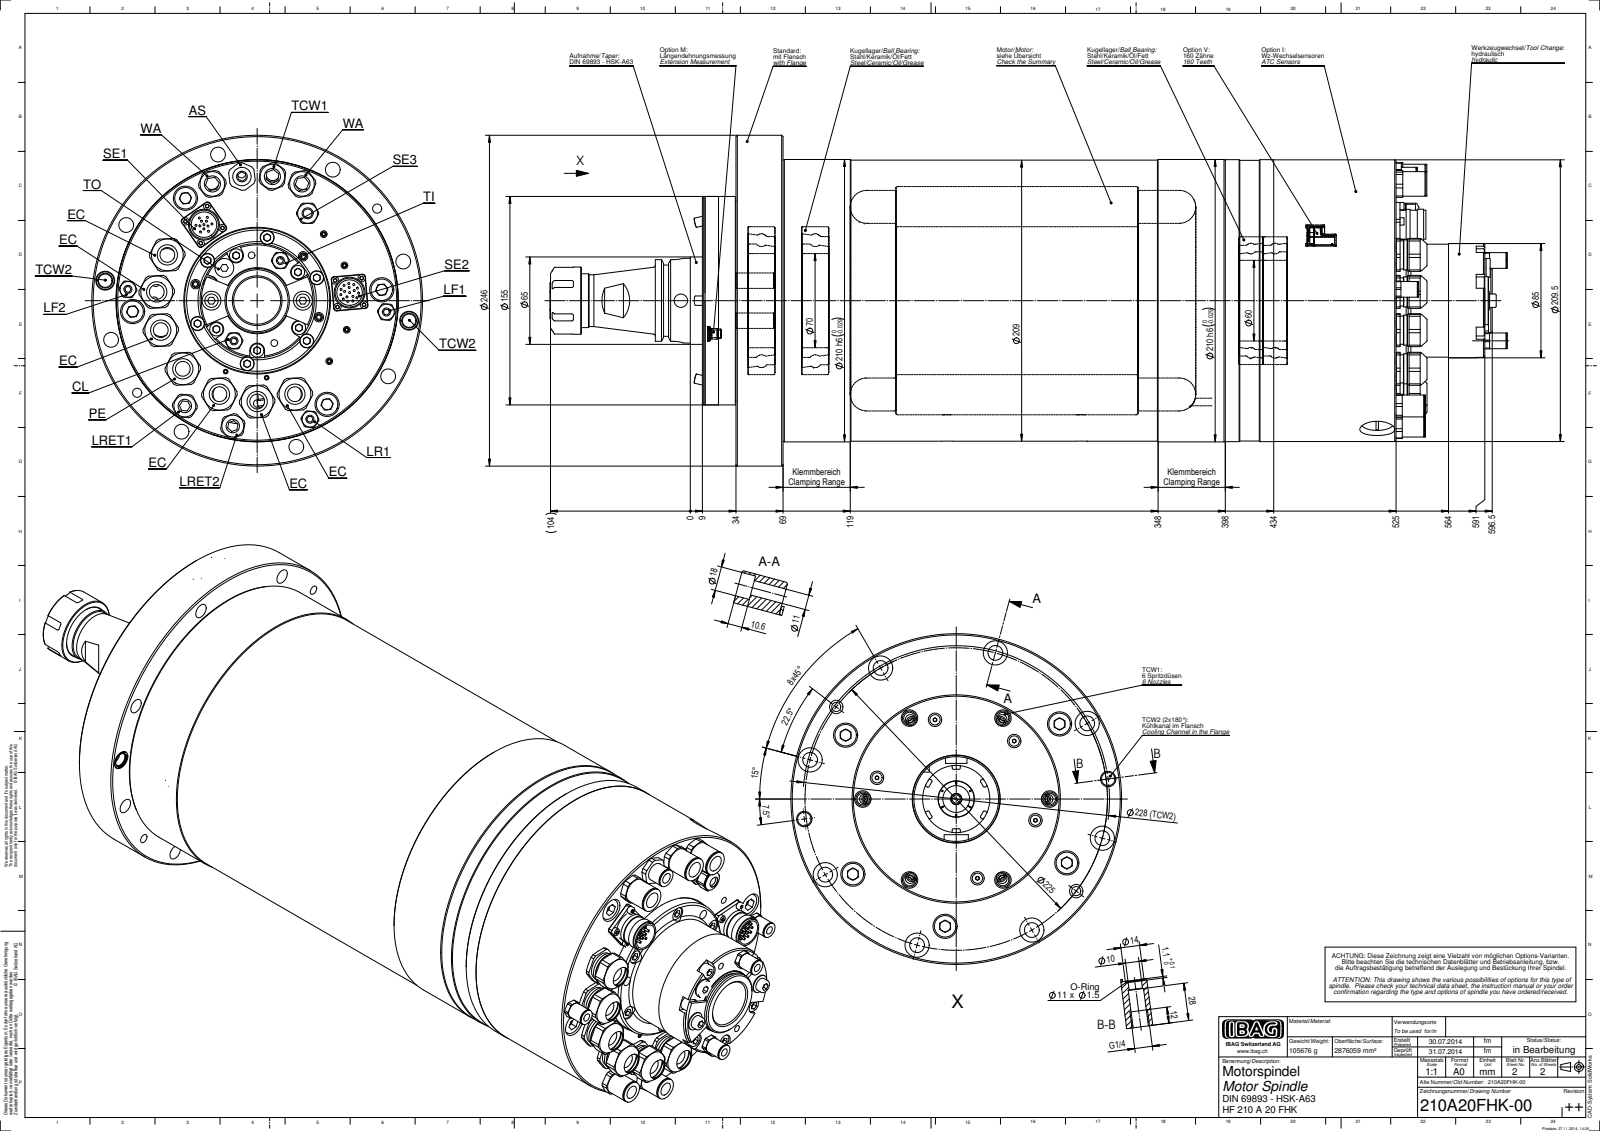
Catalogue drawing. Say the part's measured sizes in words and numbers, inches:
The part is named "210A20FHK-00". Its 3-D file was written by "SolidWorks 2014 (CONFIG_CONTROL_DESIGN)". It is 0 solids with 1647 faces: 619 planar, 704 cylindrical and 324 other. Overall it measures 28.037 by 9.685 by 9.685 inches. Round holes: 17 of diameter 0.433, 17 of diameter 0.709, 12 of diameter 0.197, 7 of diameter 0.394, 7 of diameter 0.594, 7 of diameter 0.839, 6 of diameter 0.409, 5 of diameter 0.236, 5 of diameter 1.181, 3 of diameter 0.276, 3 of diameter 0.413, 3 of diameter 0.472. Round bosses or shafts: 29 of diameter 0.059, 8 of diameter 0.394, 8 of diameter 0.217, 7 of diameter 0.933, 7 of diameter 0.878, 7 of diameter 0.825, 6 of diameter 0.276, 5 of diameter 0.461. Partial cylindrical surfaces (rounded edges, fillets, slot ends): 12 of radius 0.039, 7 of radius 0.52, 5 of radius 0.217, 5 of radius 0.26, 4 of radius 0.315, 4 of radius 0.404, 2 of radius 0.364, 1 of radius 0.325. The main face-to-face distances are 19.331, 1.378, 17.953, 2.362, 0.984, 20.315, 3.583, 16.732, 15.748, 14.37. The hole center spacings are 4.429, 3.39, 6.264, 8.184, 2.736, 3.661, 3.74, 1.741.
